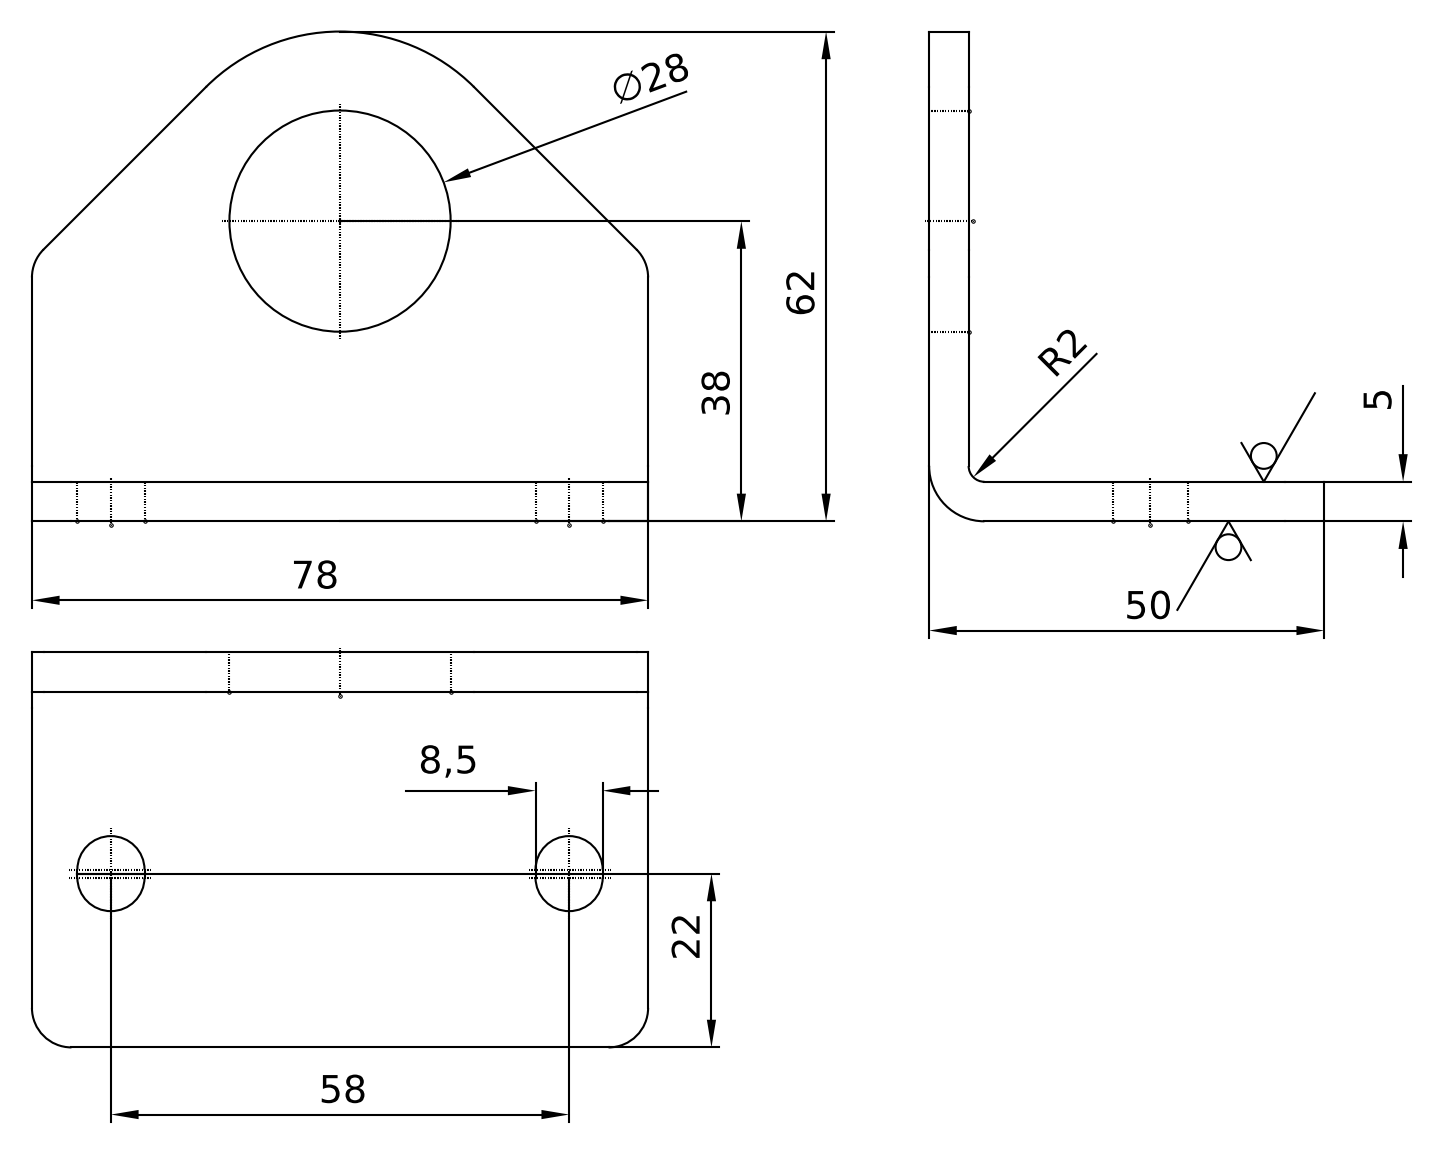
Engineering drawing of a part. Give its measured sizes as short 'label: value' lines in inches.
name: 800 062
written by: Autodesk Inventor 2024 (AUTOMOTIVE_DESIGN)
unit: in
bodies: 1 solid, 29 faces (17 planar, 12 cylindrical, 0 other)
size: 3.071 × 2.441 × 1.969
volume: 2.004 in³; area: 24.01 in²
holes: 1× ⌀1.102
rounds: 4× R0.167, 4× R0.197, 1× R0.079, 1× R0.276, 1× R0.945
face distances: 0.197, 3.071, 1.969, 1.772, 0.226, 0.561, 2.51, 2.844, 0.335, 2.283
